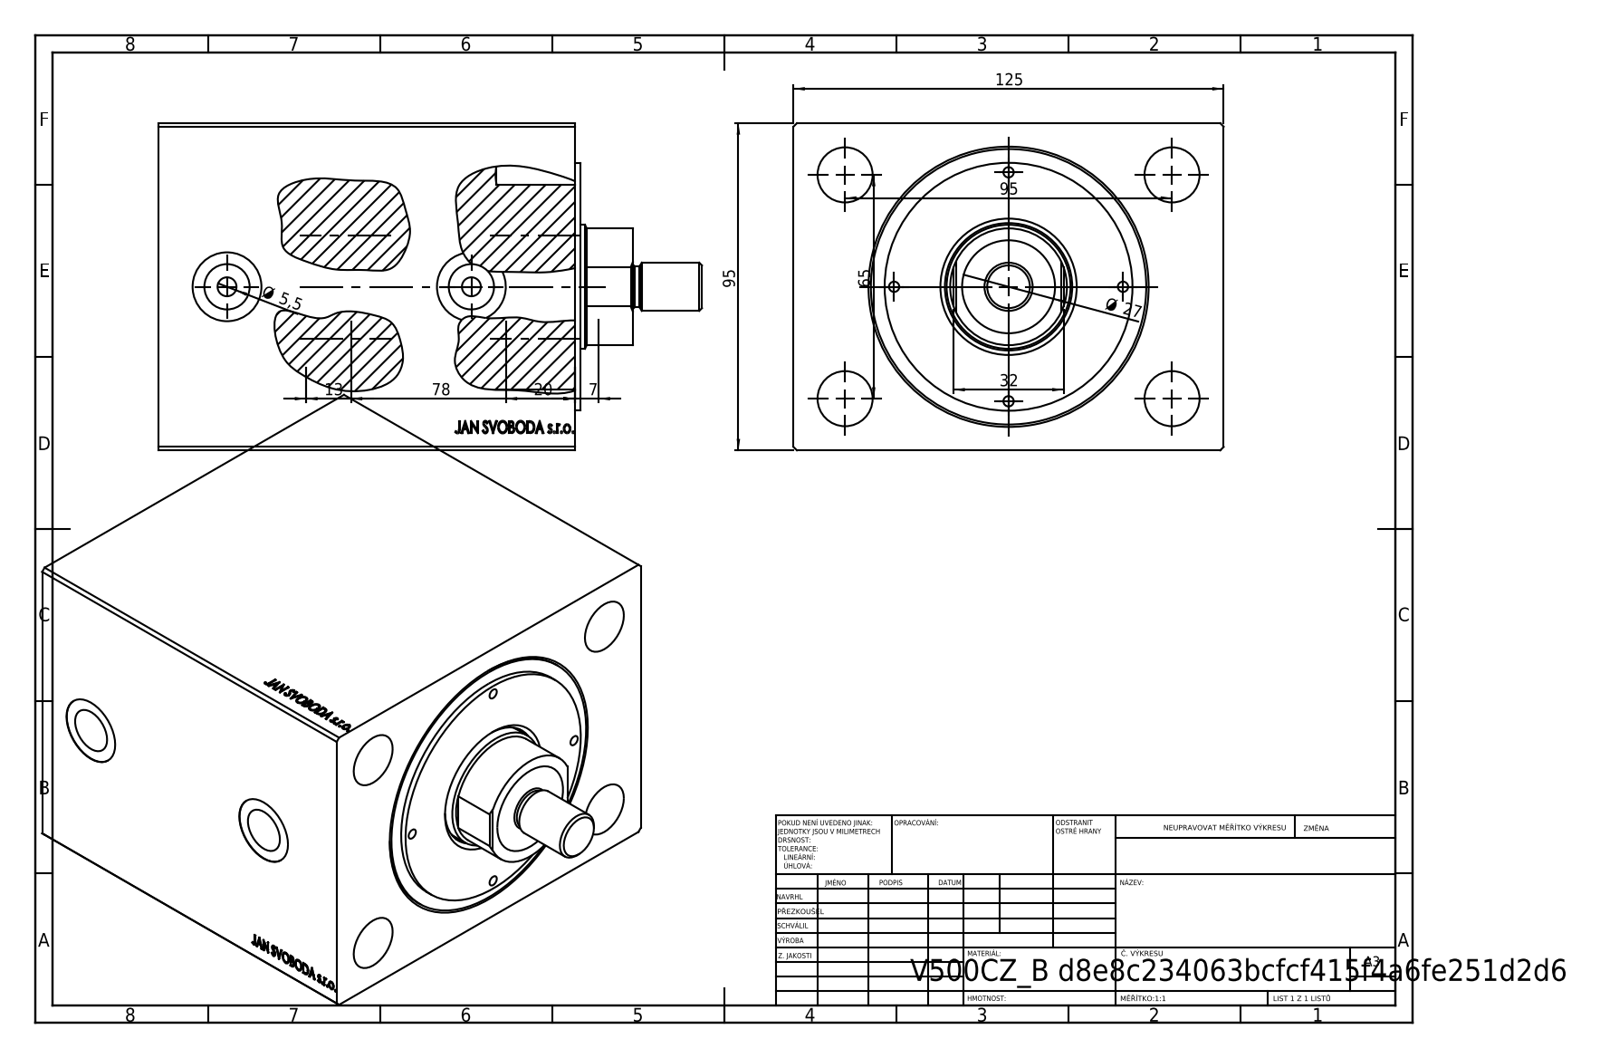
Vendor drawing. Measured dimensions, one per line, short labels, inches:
name: V500CZ_FM; V500CZ; V500CZ_vnitrni_cast_vysunovaci
written by: SolidWorks 2019 (CONFIG_CONTROL_DESIGN)
unit: in
bodies: 4 solids, 884 faces (403 planar, 63 cylindrical, 418 other)
size: 6.22 × 4.921 × 3.74
volume: 81.89 in³; area: 207.1 in²
holes: 4× ⌀0.118, 4× ⌀0.63, 2× ⌀0.217, 2× ⌀0.518, 2× ⌀0.787, 1× ⌀1.063, 1× ⌀1.417, 1× ⌀1.457, 1× ⌀2.48, 1× ⌀3.15
bosses: 1× ⌀2.835, 1× ⌀0.551, 1× ⌀0.472
rounds: 1× R0.668
face distances: 3.74, 4.921, 4.764, 2.559, 2.205, 0.394, 2.165, 4.37, 0.071, 0.465
hole spacings: 1.309, 1.397, 1.851, 1.87, 2.266, 3.193, 3.427, 2.559
